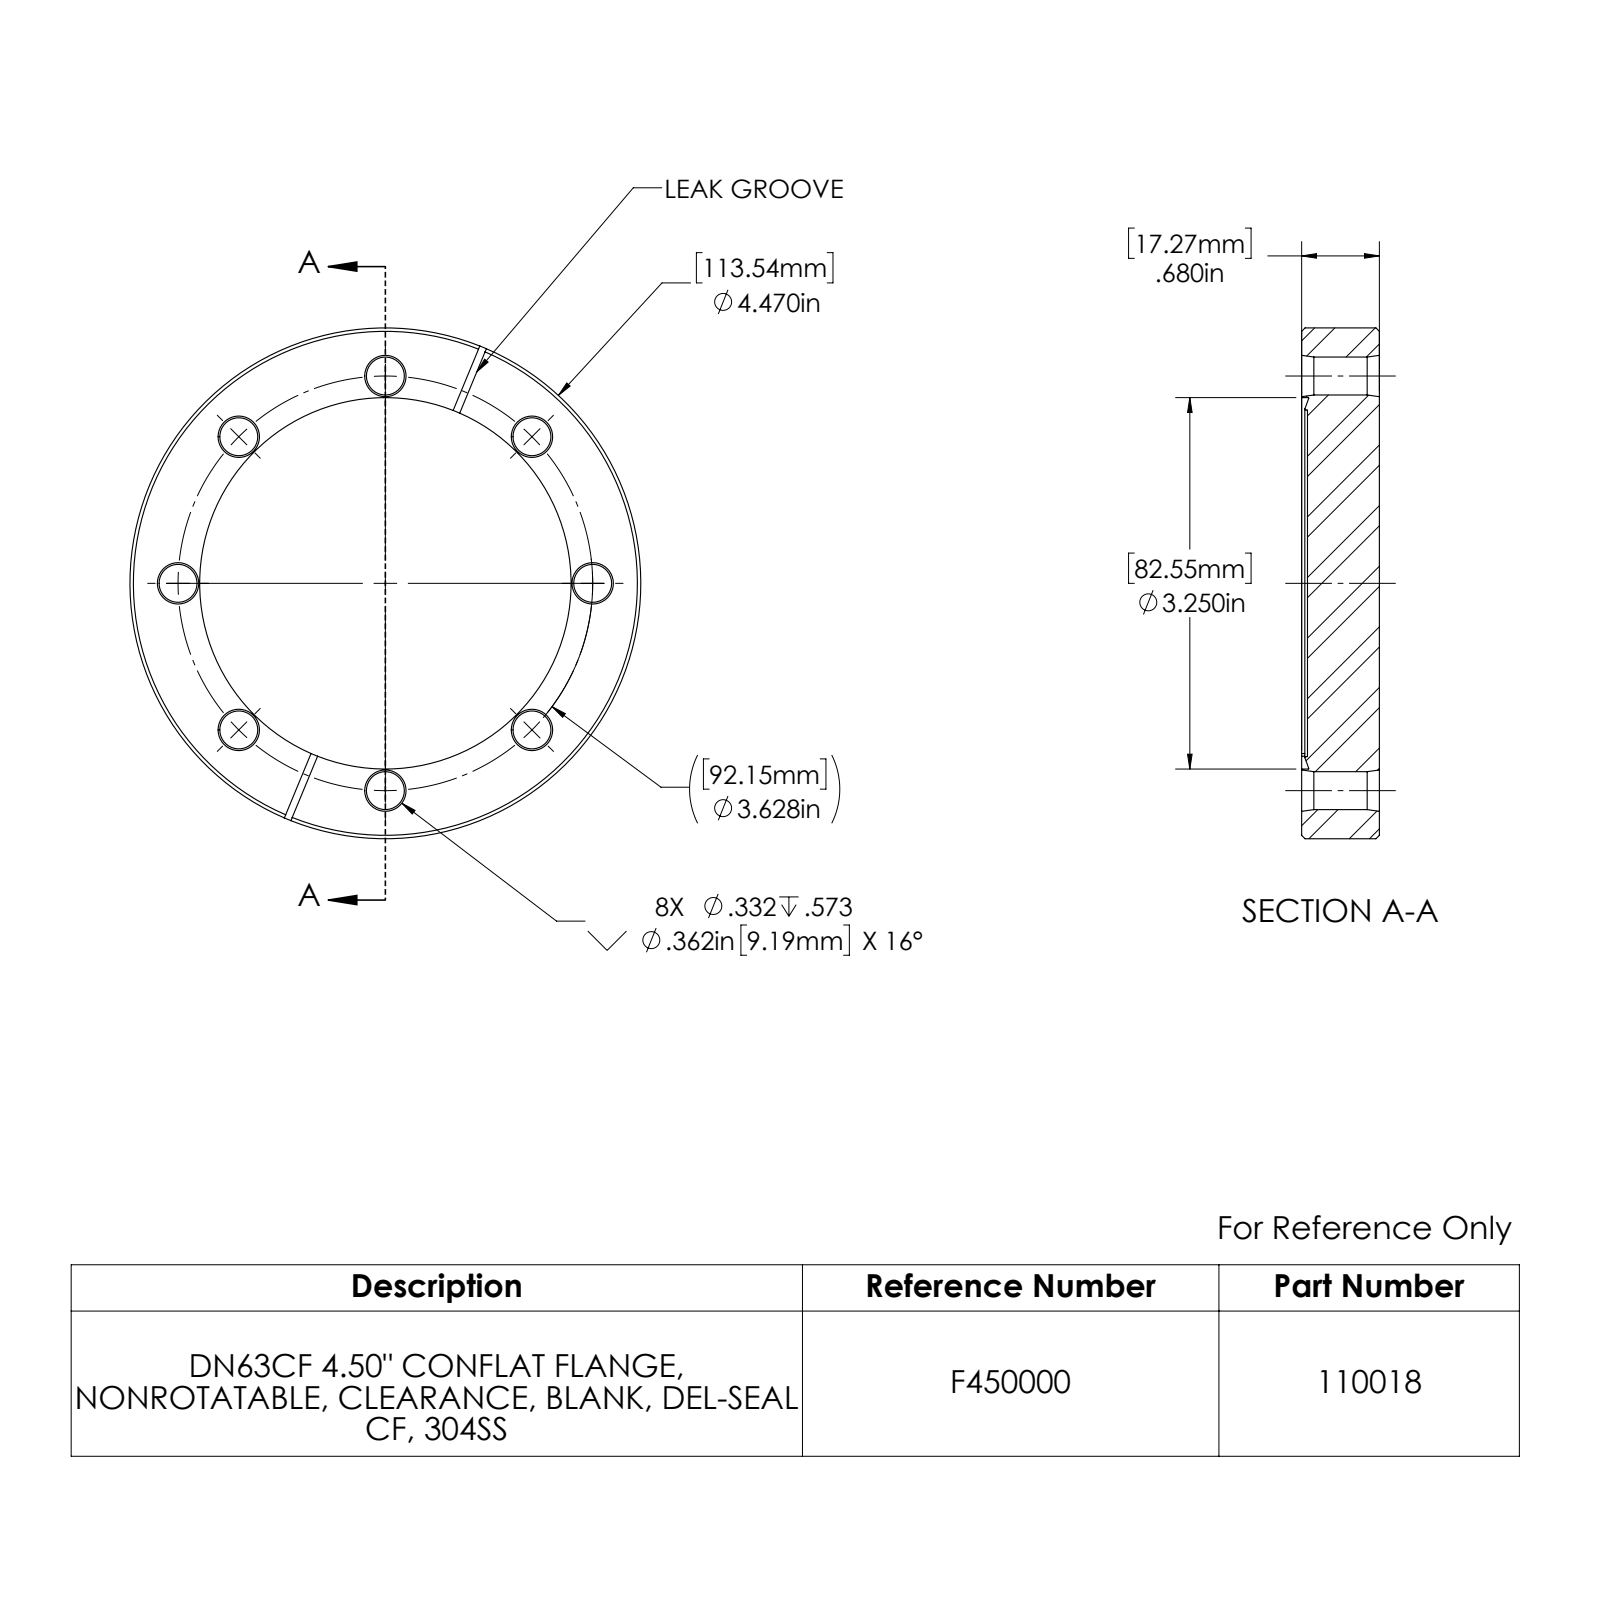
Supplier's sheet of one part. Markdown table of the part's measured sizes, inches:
| quantity | value |
| --- | --- |
| part name | 110018 |
| STEP written by | SolidWorks 2022 (AUTOMOTIVE_DESIGN) |
| units | inches |
| bodies | 1 solid, 77 faces (10 planar, 20 cylindrical, 47 other) |
| overall size | 4.47 × 4.47 × 0.68 |
| volume | 9.753 in³ |
| surface area | 45.51 in² |
| round holes (diameter × count) | 0.332 × 8, 3.25 × 1 |
| round bosses / shafts (diameter × count) | 4.47 × 1 |
| main face-to-face distances | 0.629, 0.051, 0.68, 0.052, 0.628, 0.062, 0.063, 0.062, 0.061 |
| hole center spacings | 1.389, 1.814, 3.352, 2.565, 2.566, 3.628, 3.628 |
